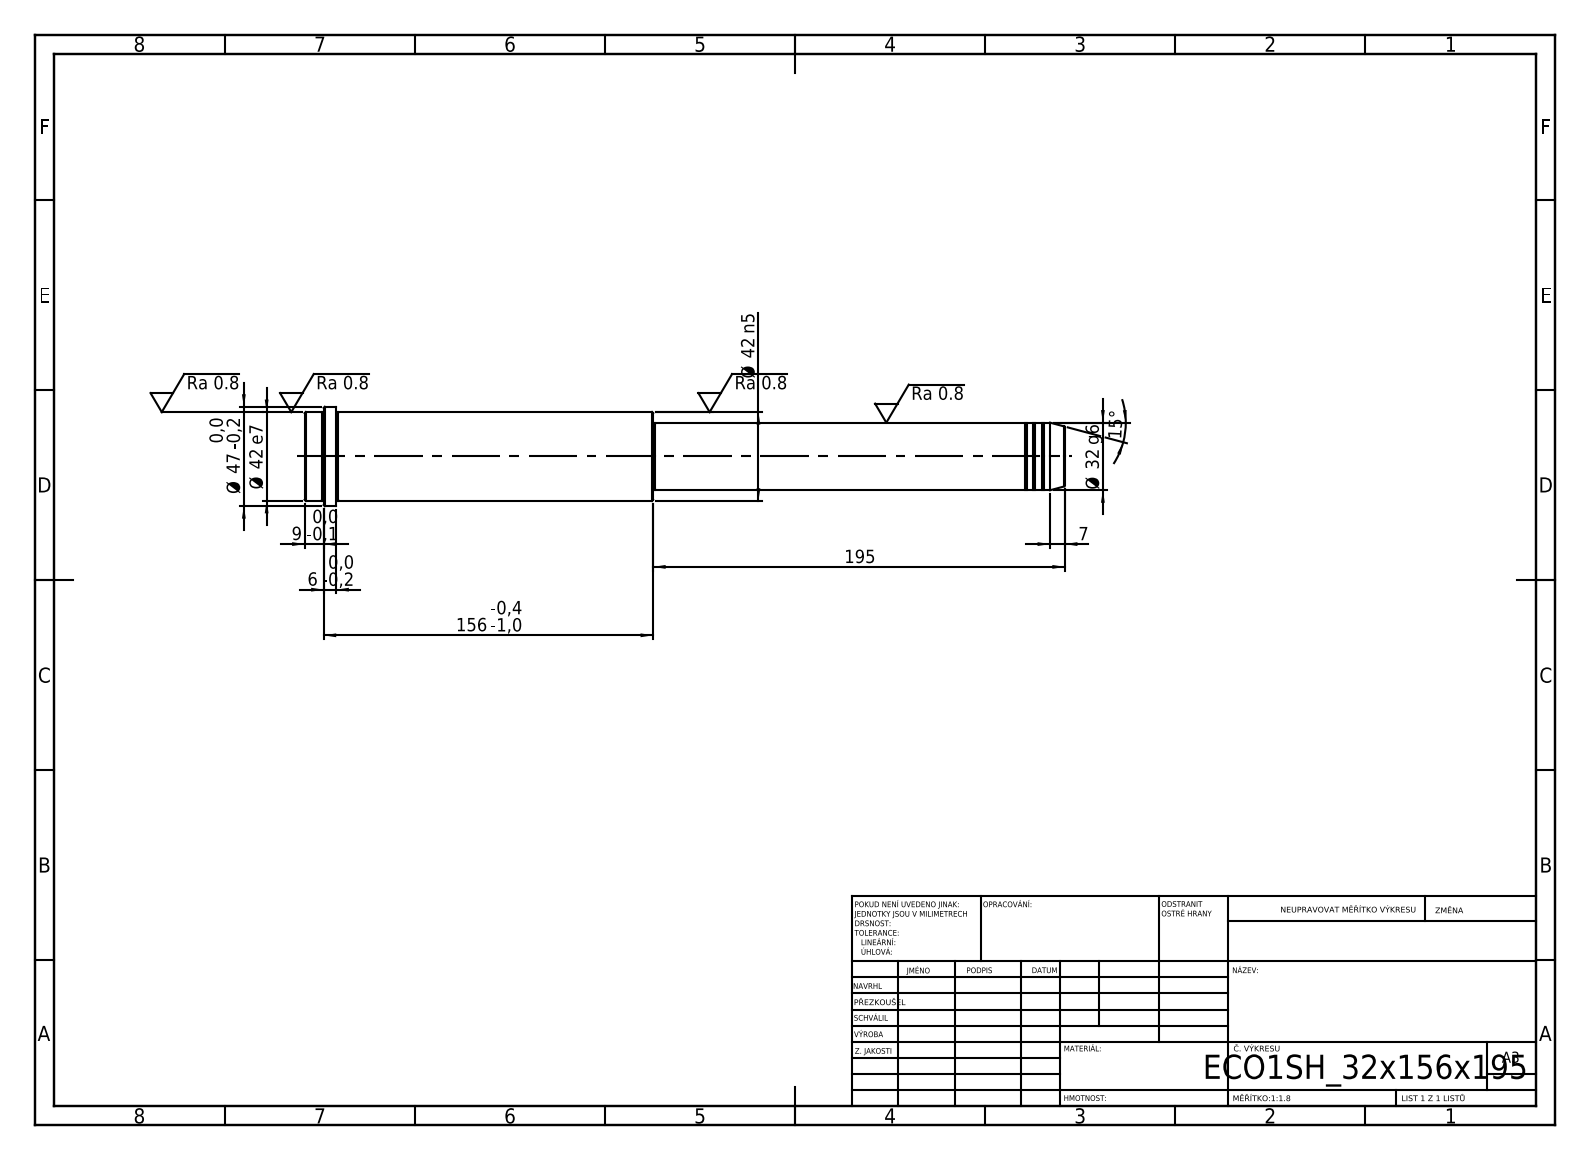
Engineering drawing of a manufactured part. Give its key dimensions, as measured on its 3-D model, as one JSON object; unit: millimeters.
{"step_written_by": "SolidWorks 2019 (CONFIG_CONTROL_DESIGN)", "units": "millimeters", "bodies": {"solids": 1, "faces": 52, "planar": 6, "cylindrical": 16, "other": 30}, "overall_size": [360, 47, 47], "volume_mm3": 386567, "surface_area_mm2": 45015, "round_bosses_or_shafts": [[47, 1], [42, 1], [32, 1], [31, 1]], "face_to_face_distances": [360, 195, 165, 345, 150, 15, 351, 156, 6, 9]}
